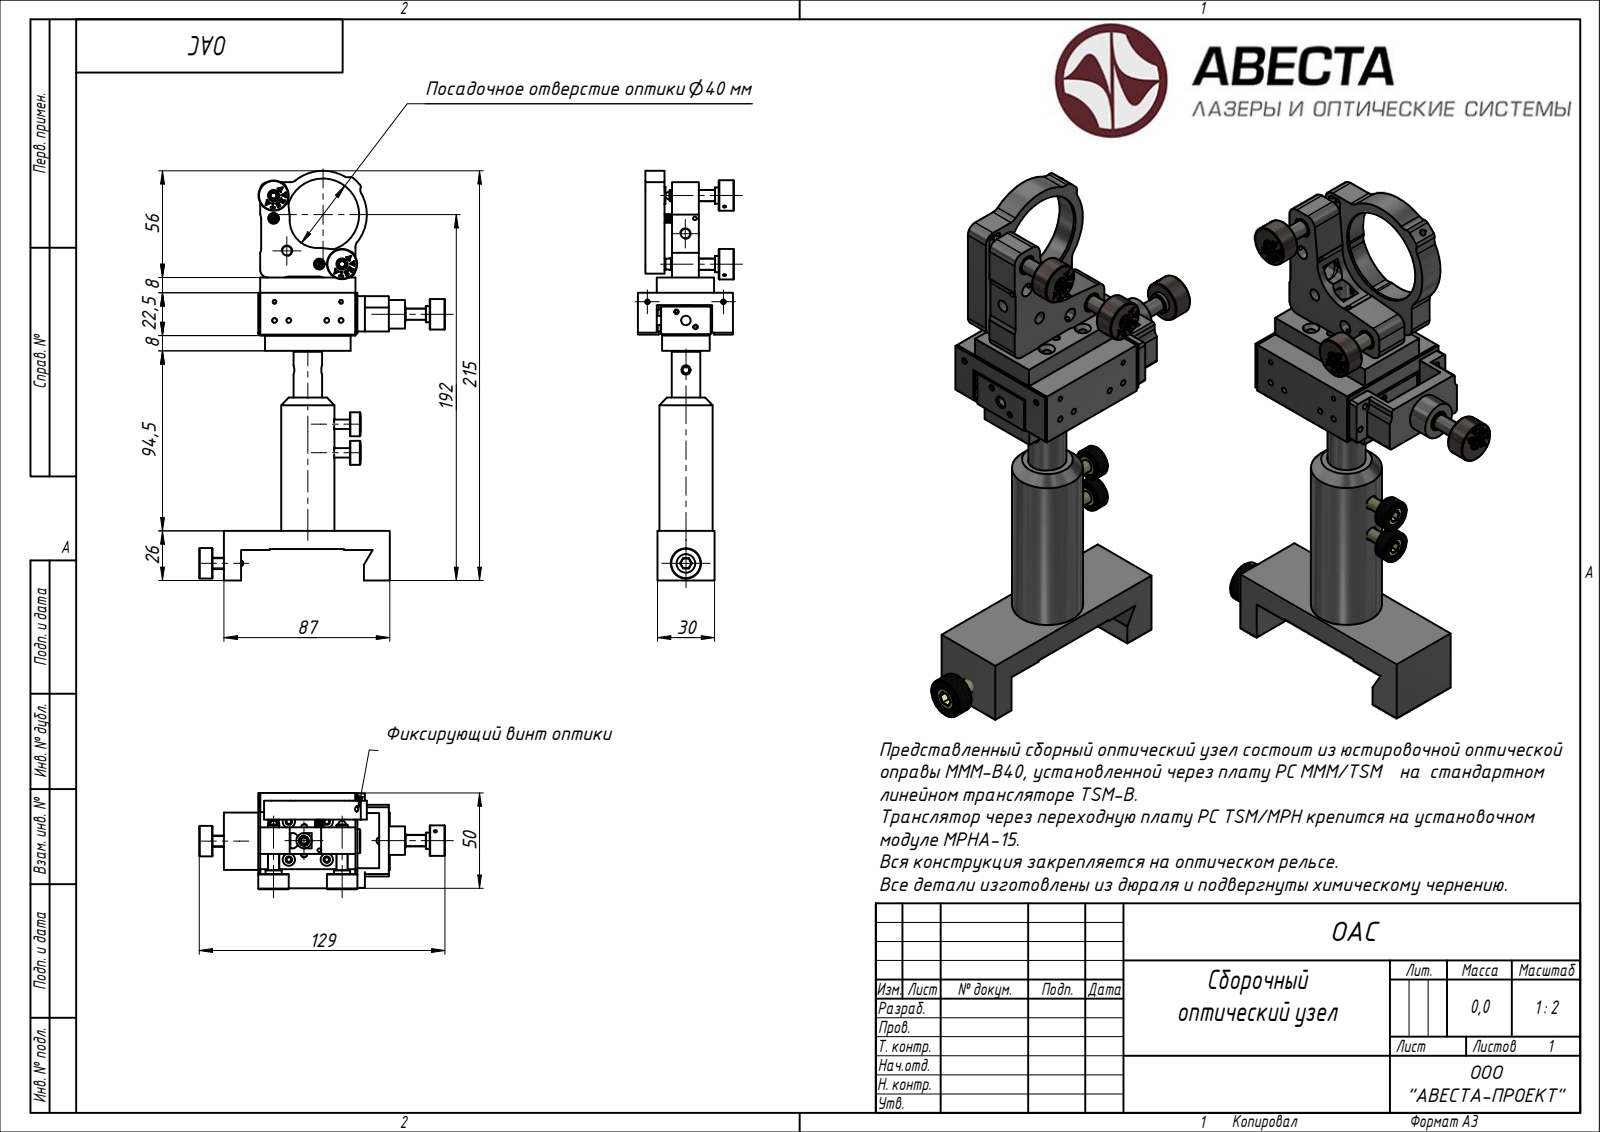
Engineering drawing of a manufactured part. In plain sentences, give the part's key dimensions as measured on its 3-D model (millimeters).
The part is named "Block 01; Block 03; Block 04". Its 3-D file was written by "ST-DEVELOPER v15 (AUTOMOTIVE_DESIGN)". It is 35 solids with 1638 faces: 0 planar, 0 cylindrical and 1638 other. Overall it measures 215 by 127 by 50.5 millimeters.
